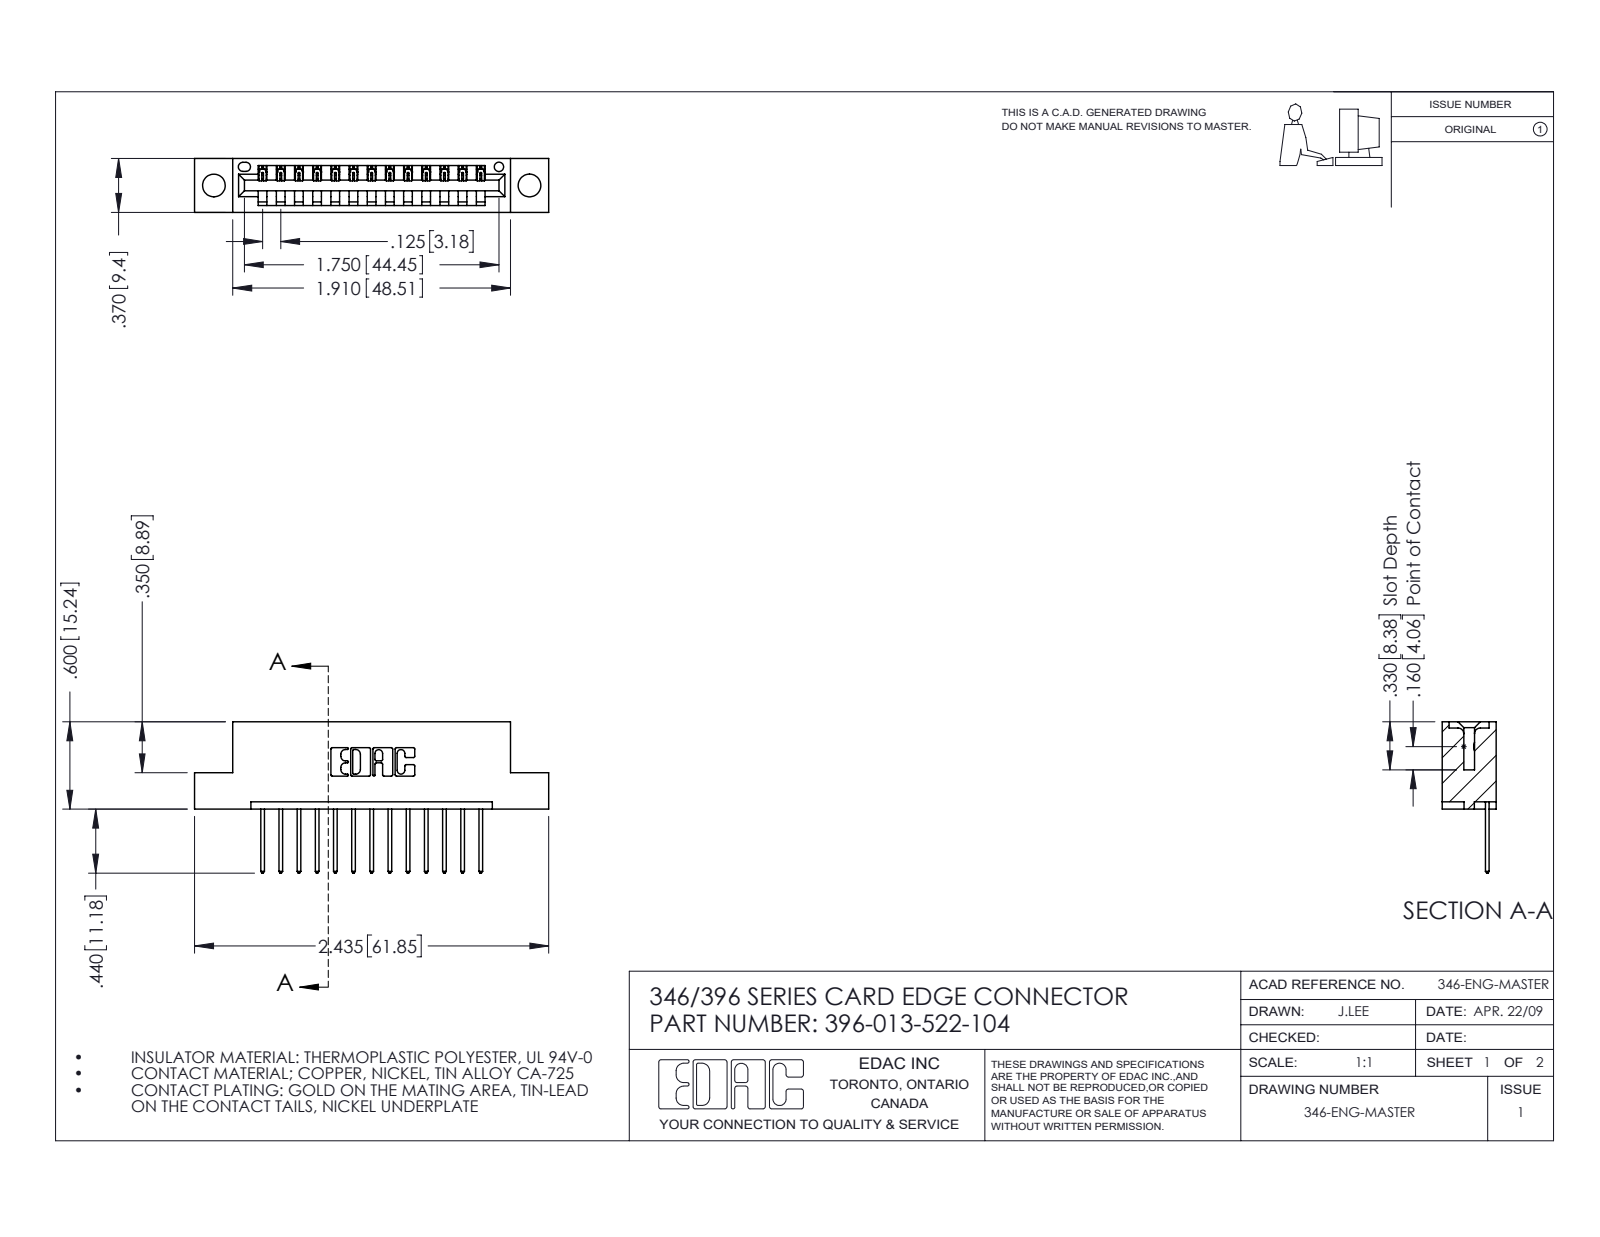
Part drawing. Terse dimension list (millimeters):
name: 396-013-522-104; 346 Part_Flush Mounting Lugs - 0.156 Dia-TH; 345-292-001_345-293-122
written by: SolidWorks 2016 (CONFIG_CONTROL_DESIGN)
unit: mm
bodies: 14 solids, 876 faces (596 planar, 280 cylindrical, 0 other)
size: 61.8 × 26.4 × 9.4
volume: 5 640 mm³; area: 6 581 mm²
holes: 2× ⌀4, 1× ⌀1.6
rounds: 26× R0.2, 26× R0.3, 22× R0.3, 6× R0.2, 6× R0.8, 3× R0.7, 2× R0.8, 2× R1
face distances: 6.4, 1.2, 8.2, 9.4, 1.8, 7.6, 0.6, 3.8, 5.6, 2.5
hole spacings: 6.2, 49.9, 55.1
